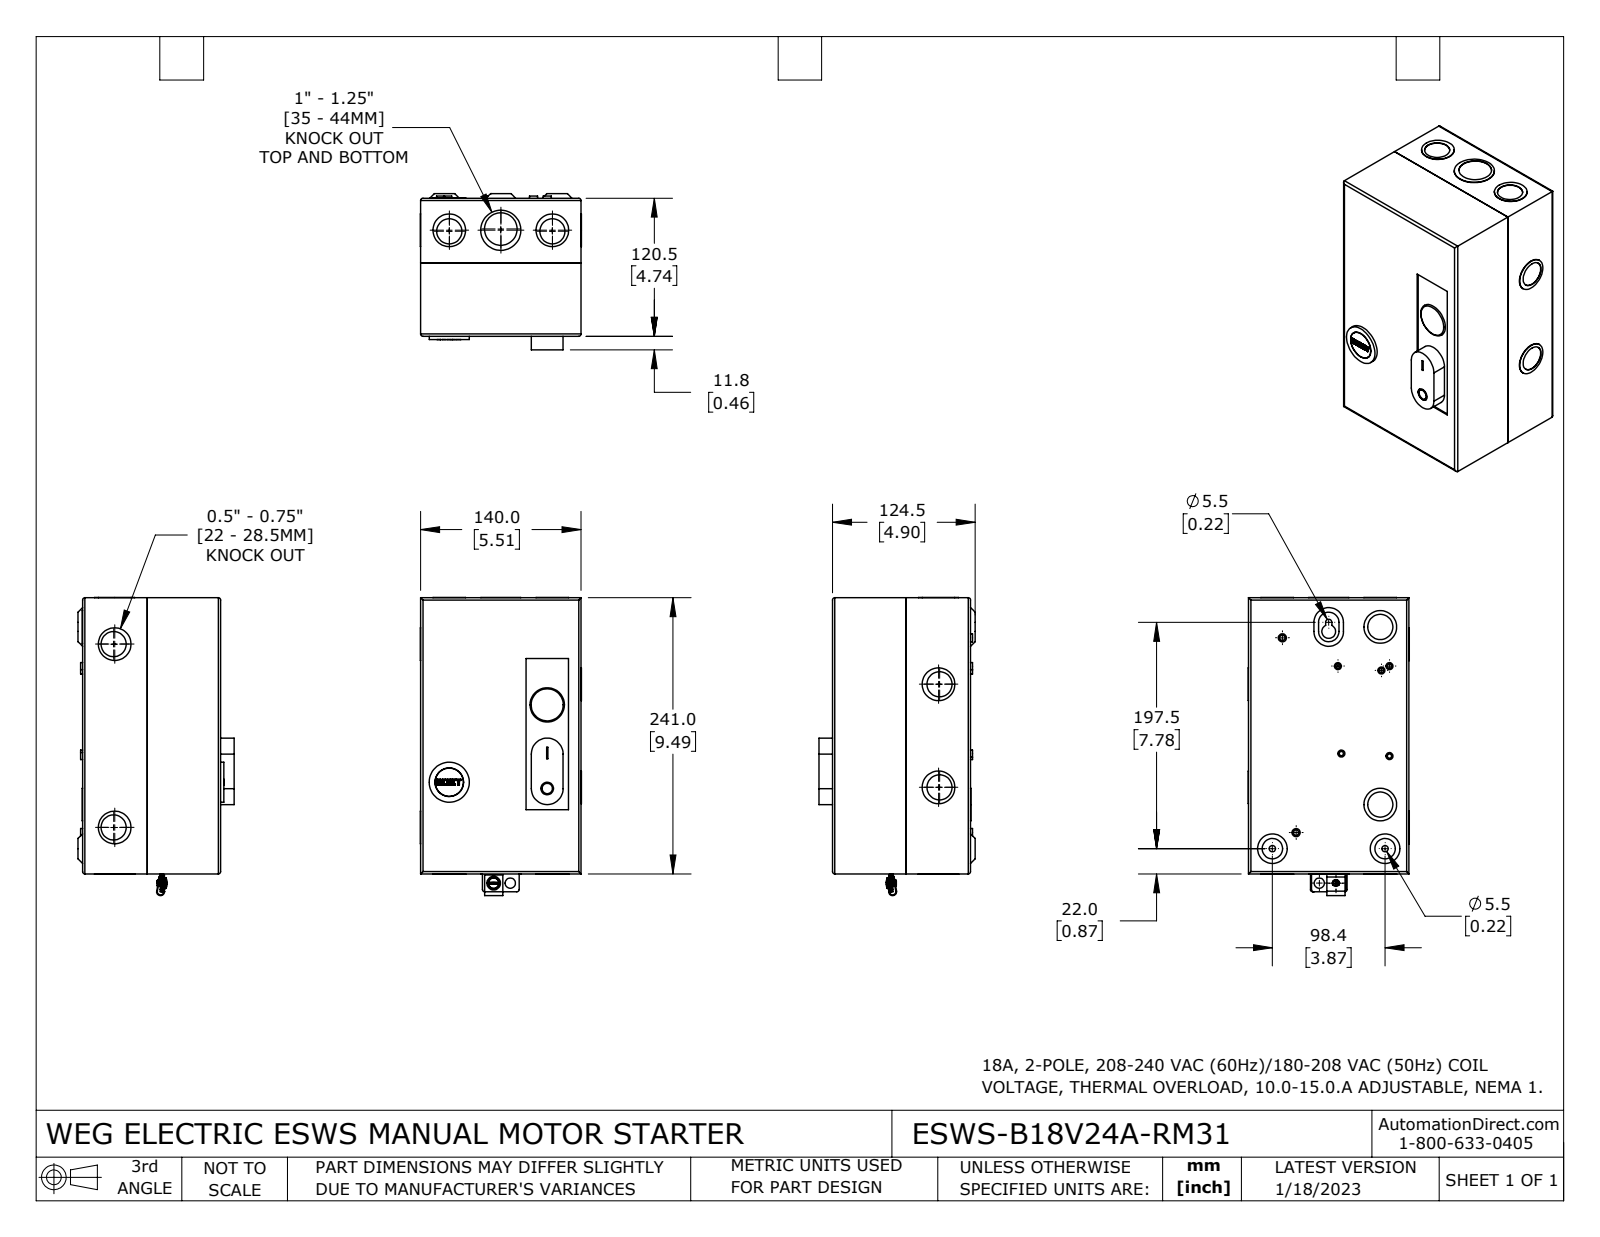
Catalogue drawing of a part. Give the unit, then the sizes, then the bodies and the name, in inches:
Units: inches
Overall size (bounding box): 10.248 × 5.535 × 5.366
Round holes (diameter × count): ⌀0.146 ×5, ⌀0.864 ×4, ⌀0.183 ×2, ⌀0.217 ×2, ⌀0.354 ×2, ⌀0.864 ×2, ⌀0.866 ×2, ⌀0.886 ×2, ⌀0.256 ×1, ⌀0.303 ×1, ⌀0.433 ×1, ⌀0.469 ×1
Round bosses / shafts (diameter × count): ⌀1.124 ×6, ⌀0.24 ×5, ⌀1.122 ×2, ⌀0.278 ×2, ⌀1.38 ×1, ⌀1.378 ×1, ⌀1.193 ×1, ⌀1.148 ×1
Partial cylindrical surfaces — rounded edges, fillets, slot ends (radius × count): R0.004 ×34, R0.079 ×13, R0.031 ×4, R0.108 ×3, R0.059 ×2, R0.075 ×2, R0.122 ×2, R0.138 ×2
Main face-to-face distances: 0.047, 4.697, 5.465, 4.65, 9.441, 4.744, 5.417, 5.512, 0.071, 0.063
Hole centre spacings: 0.571, 1.378, 1.773, 3.387, 3.543, 4.921, 5.995, 7.484
Volume: 16.23 in³ · Surface area: 585.2 in²
Bodies: 7 solids, 435 faces (168 planar, 230 cylindrical, 37 other)
Part name (STEP PRODUCT): ESWS-B18V24A-RM31
STEP written by: SolidWorks 2021 (CONFIG_CONTROL_DESIGN)
